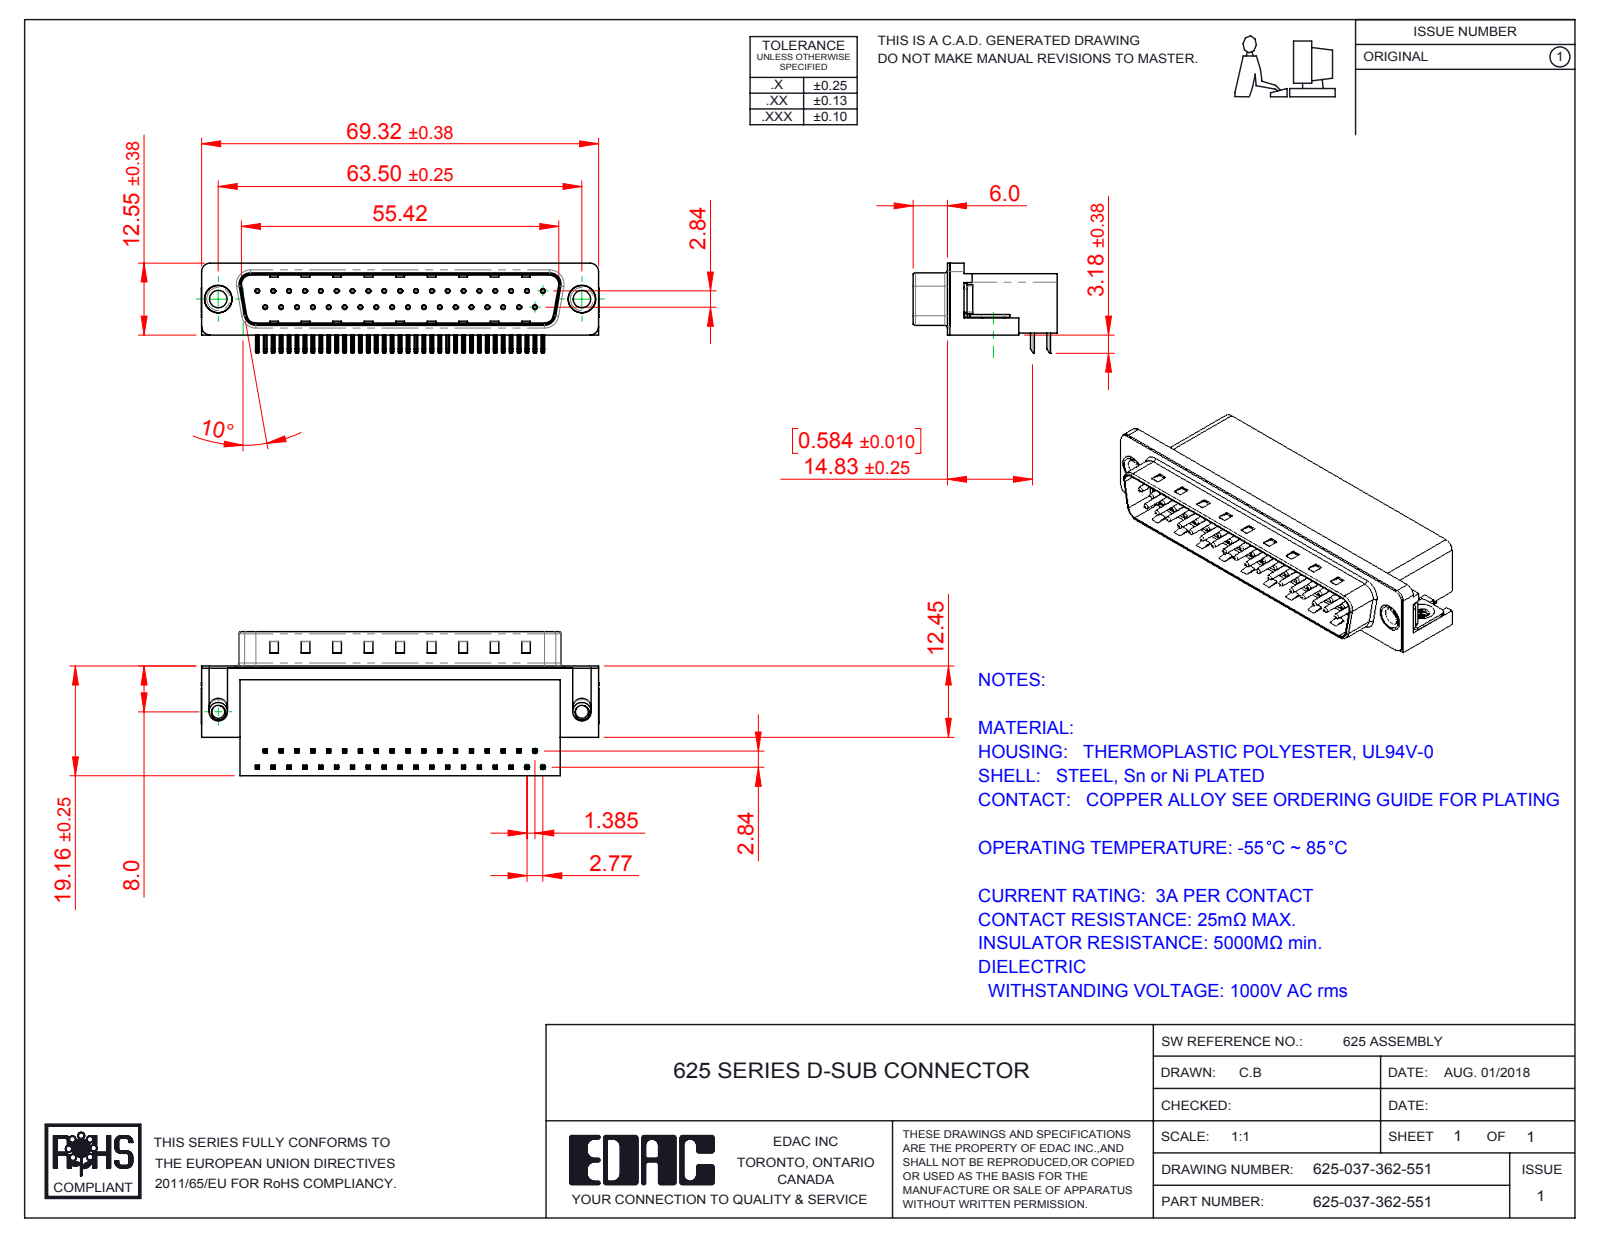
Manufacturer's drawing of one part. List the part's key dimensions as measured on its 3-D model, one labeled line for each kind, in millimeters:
Part name (STEP PRODUCT): 625 Contact Bottom; 625 Thru Hole Rivet; 625 4-40 Threaded Board Mount; 625 Contact Top (+3 more)
STEP written by: SolidWorks 2016 (CONFIG_CONTROL_DESIGN)
Units: millimetres
Bodies: 43 solids, 3193 faces (2015 planar, 911 cylindrical, 267 other)
Overall size (bounding box): 69.4 × 25.16 × 15.73
Volume: 12 599 mm³ · Surface area: 11 810 mm²
Round holes (diameter × count): ⌀0.35 ×37, ⌀0.8 ×37, ⌀2.26 ×2, ⌀3.05 ×2, ⌀4 ×2, ⌀4.8 ×2, ⌀5 ×2
Round bosses / shafts (diameter × count): ⌀0.75 ×37, ⌀4.9 ×2, ⌀4.75 ×2, ⌀3.85 ×2, ⌀3.26 ×2
Partial cylindrical surfaces — rounded edges, fillets, slot ends (radius × count): R0.25 ×156, R0.12 ×74, R1 ×16, R0.5 ×9, R1.6 ×8, R1.5 ×7, R0.9 ×4, R2 ×4
Main face-to-face distances: 10.34, 0.4, 18.76, 8.76, 19.16, 2.84, 2.09, 10.1, 1.74, 8.36
Hole centre spacings: 3.16, 2.77, 5.54, 8.31, 11.08, 13.85, 19.39, 22.16
